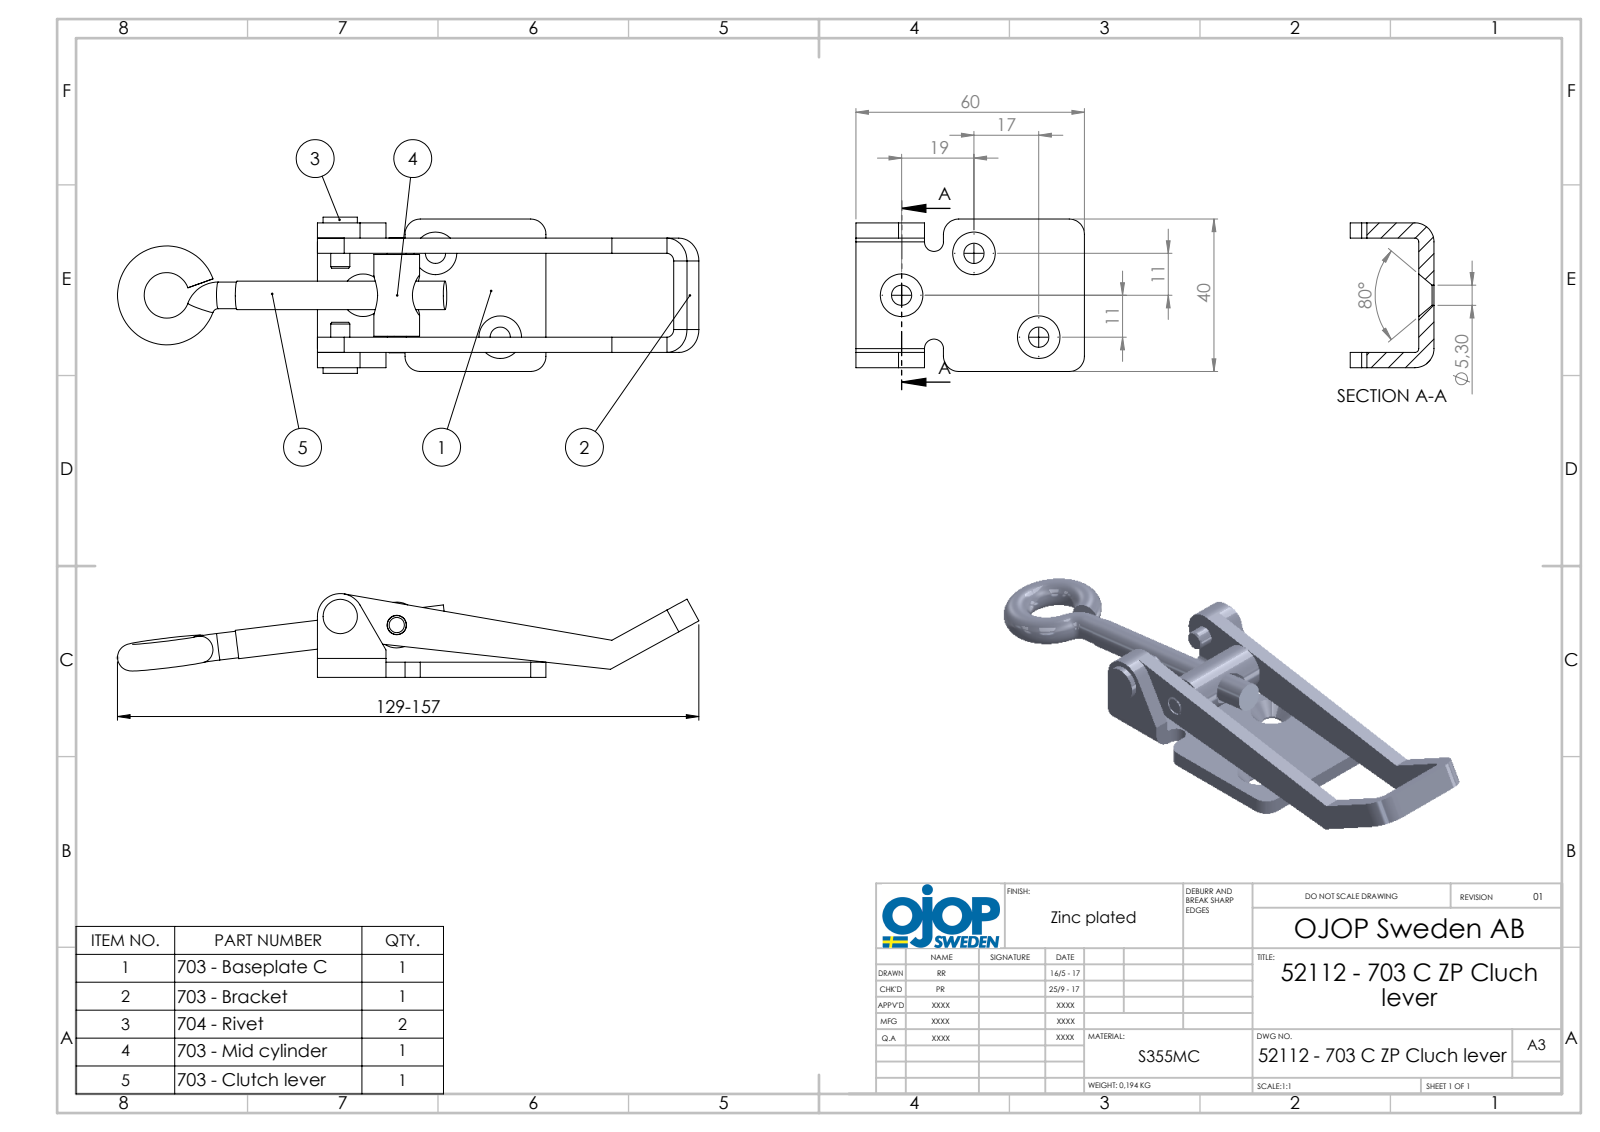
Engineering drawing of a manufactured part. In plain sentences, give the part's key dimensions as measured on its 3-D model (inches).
The part is named "703 - Bygel; 703 - Platta C; 703 - öglebult; 704 - Rivet Gradin (+2 more)". Its 3-D file was written by "SolidWorks 2015 (AUTOMOTIVE_DESIGN)". It is 6 solids with 144 faces: 57 planar, 61 cylindrical and 26 other. Overall it measures 6.009 by 1.614 by 0.866 inches. Its volume is 1.541 cubic inches and its surface area 26.77 square inches. Round holes: 3 of diameter 0.209, 2 of diameter 0.201, 1 of diameter 0.283, 1 of diameter 0.303. Round bosses or shafts: 2 of diameter 0.276, 2 of diameter 0.197, 1 of diameter 0.472, 1 of diameter 0.354, 1 of diameter 0.295. Partial cylindrical surfaces (rounded edges, fillets, slot ends): 4 of radius 0.157, 3 of radius 0.236, 2 of radius 0.039, 2 of radius 0.079, 2 of radius 0.098, 2 of radius 0.197. The main face-to-face distances are 0.157, 1.024, 1.181, 0.866, 0.315, 1.339, 0.256, 0.197, 0.039, 0.354. The hole center spacings are 0.591, 0.864, 1.094, 1.482.
